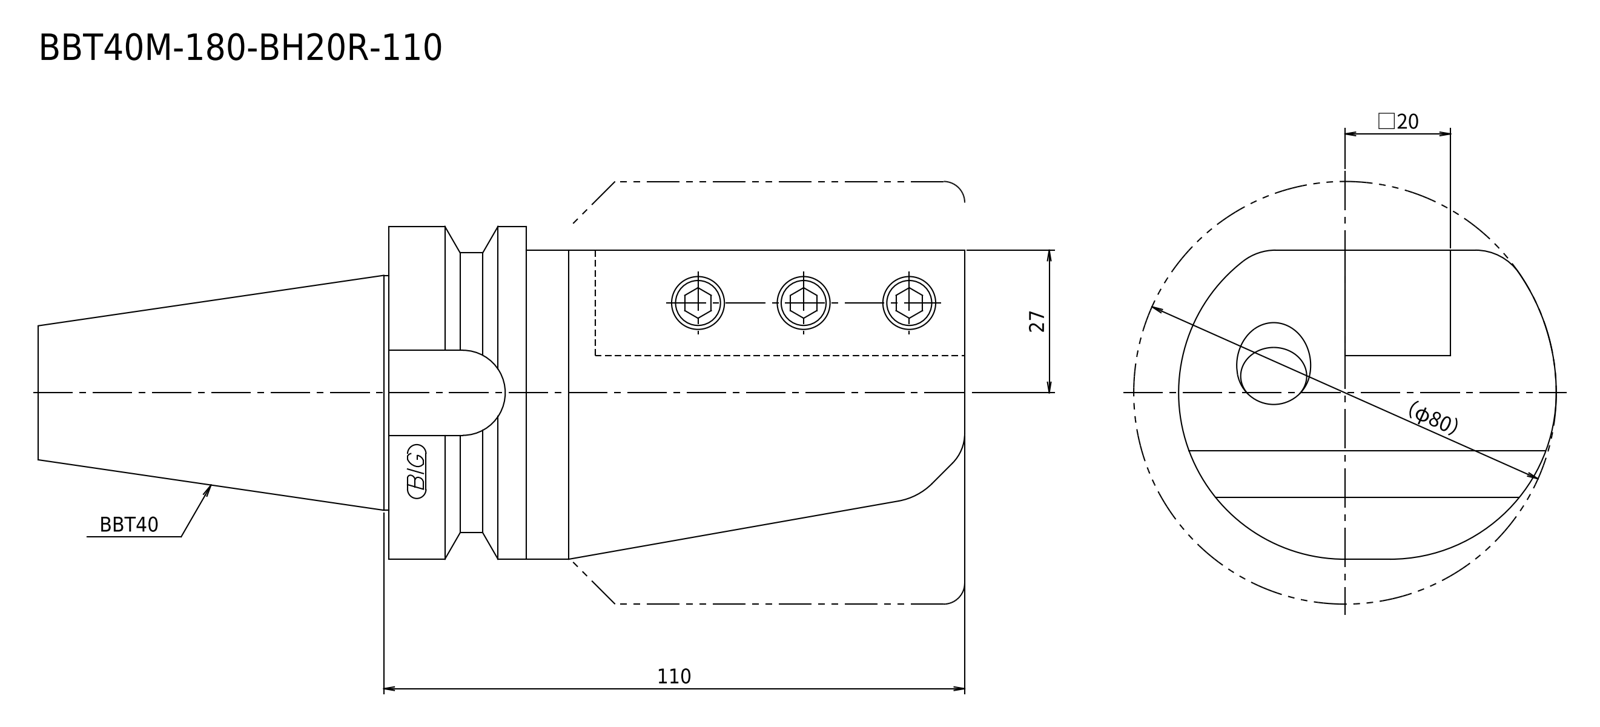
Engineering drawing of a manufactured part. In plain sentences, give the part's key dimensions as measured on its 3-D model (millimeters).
Its 3-D file was written by "Kubotek KeyCreator 2011 V10.0.2 (22737) (automotive_design)". It is 1 solid with 23 faces: 11 planar, 7 cylindrical and 5 other. Overall it measures 175.4 by 71.5 by 63 millimeters. Its volume is 379 469 cubic millimeters and its surface area 38 666 square millimeters. Round bosses or shafts: 1 of diameter 63, 1 of diameter 53, 1 of diameter 44.45. Partial cylindrical surfaces (rounded edges, fillets, slot ends): 1 of radius 31.5, 1 of radius 40. The main face-to-face distances are 20, 109, 175.4, 66.4, 70, 39, 105.4, 83, 13, 26.
